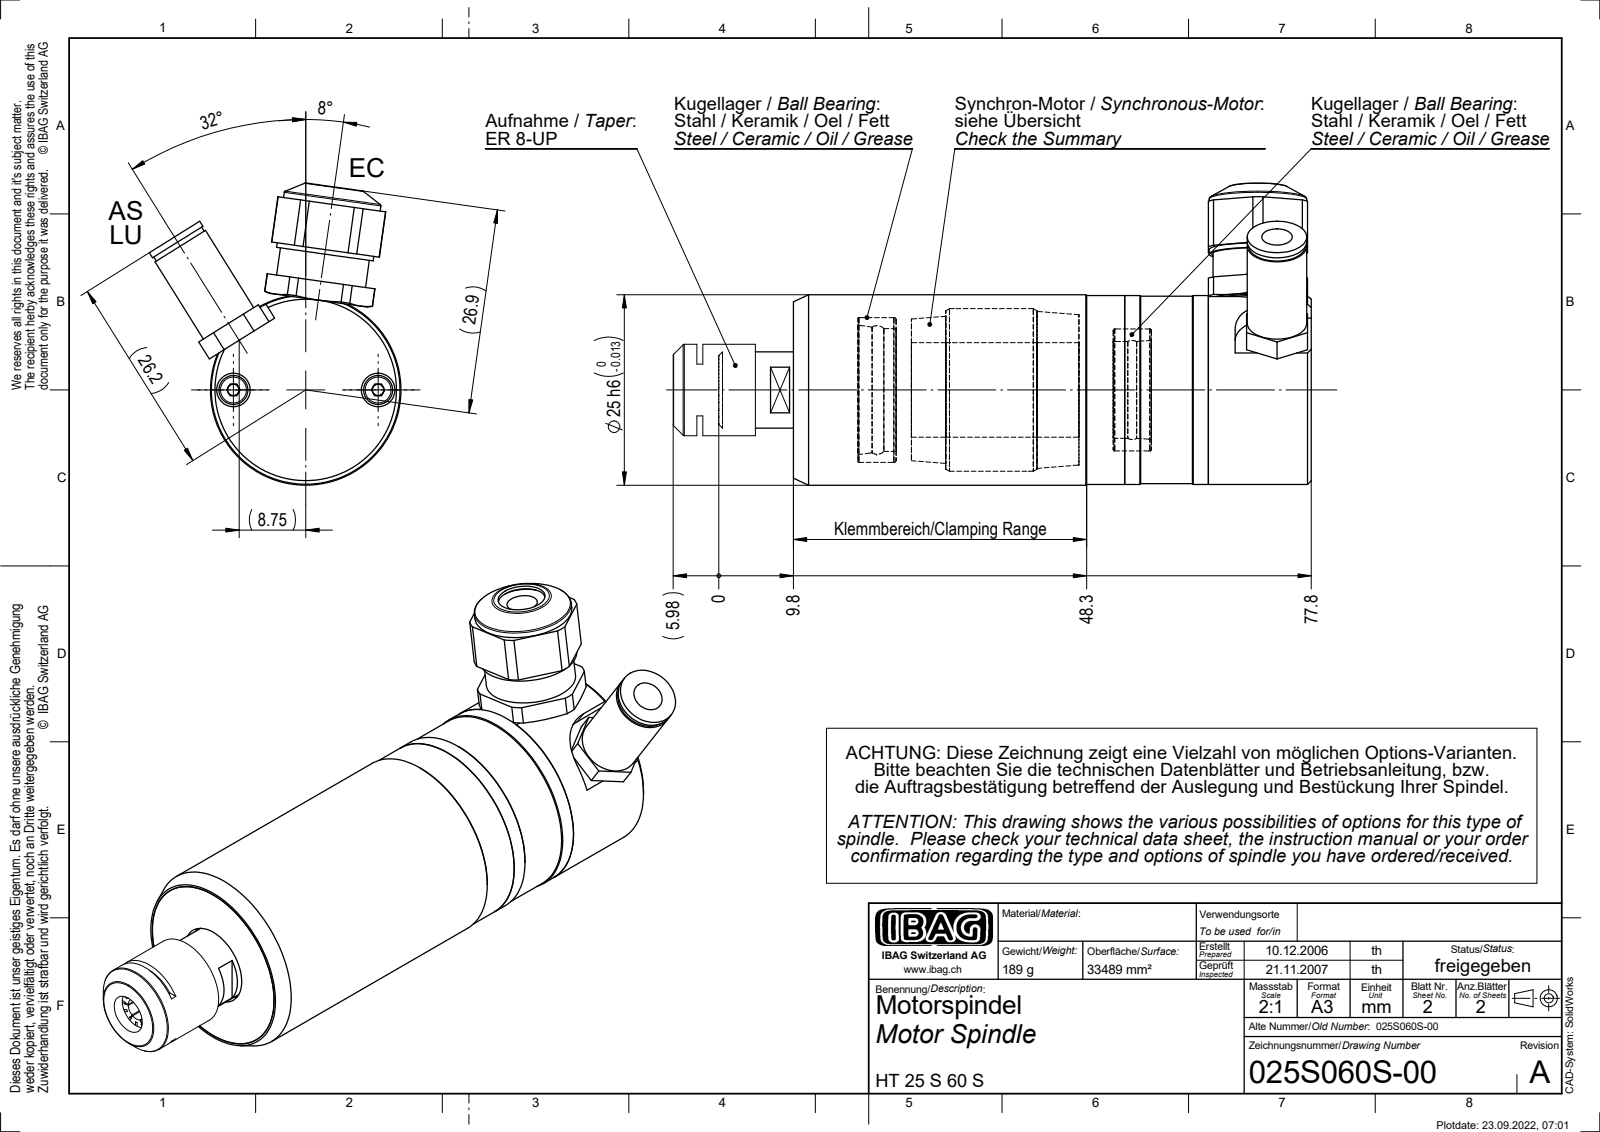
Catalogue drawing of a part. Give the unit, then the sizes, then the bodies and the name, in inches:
Units: inches
Overall size (bounding box): 3.298 × 1.561 × 1.301
Round holes (diameter × count): ⌀0.157 ×2, ⌀0.173 ×2, ⌀0.118 ×1, ⌀0.205 ×1, ⌀0.244 ×1, ⌀0.417 ×1
Round bosses / shafts (diameter × count): ⌀0.15 ×2, ⌀0.984 ×1, ⌀0.976 ×1, ⌀0.969 ×1, ⌀0.89 ×1, ⌀0.504 ×1, ⌀0.472 ×1, ⌀0.464 ×1
Partial cylindrical surfaces — rounded edges, fillets, slot ends (radius × count): R0.281 ×2, R0.167 ×1, R0.217 ×1
Main face-to-face distances: 2.677, 0.071, 2.606, 1.713, 1.642, 0.965, 2.146, 2.075, 0.433, 0.531
Hole centre spacings: 0.374, 0.748
Bodies: 0 solids, 211 faces (96 planar, 68 cylindrical, 47 other)
Part name (STEP PRODUCT): 025S060S-00A
STEP written by: SolidWorks 2010 (CONFIG_CONTROL_DESIGN)
